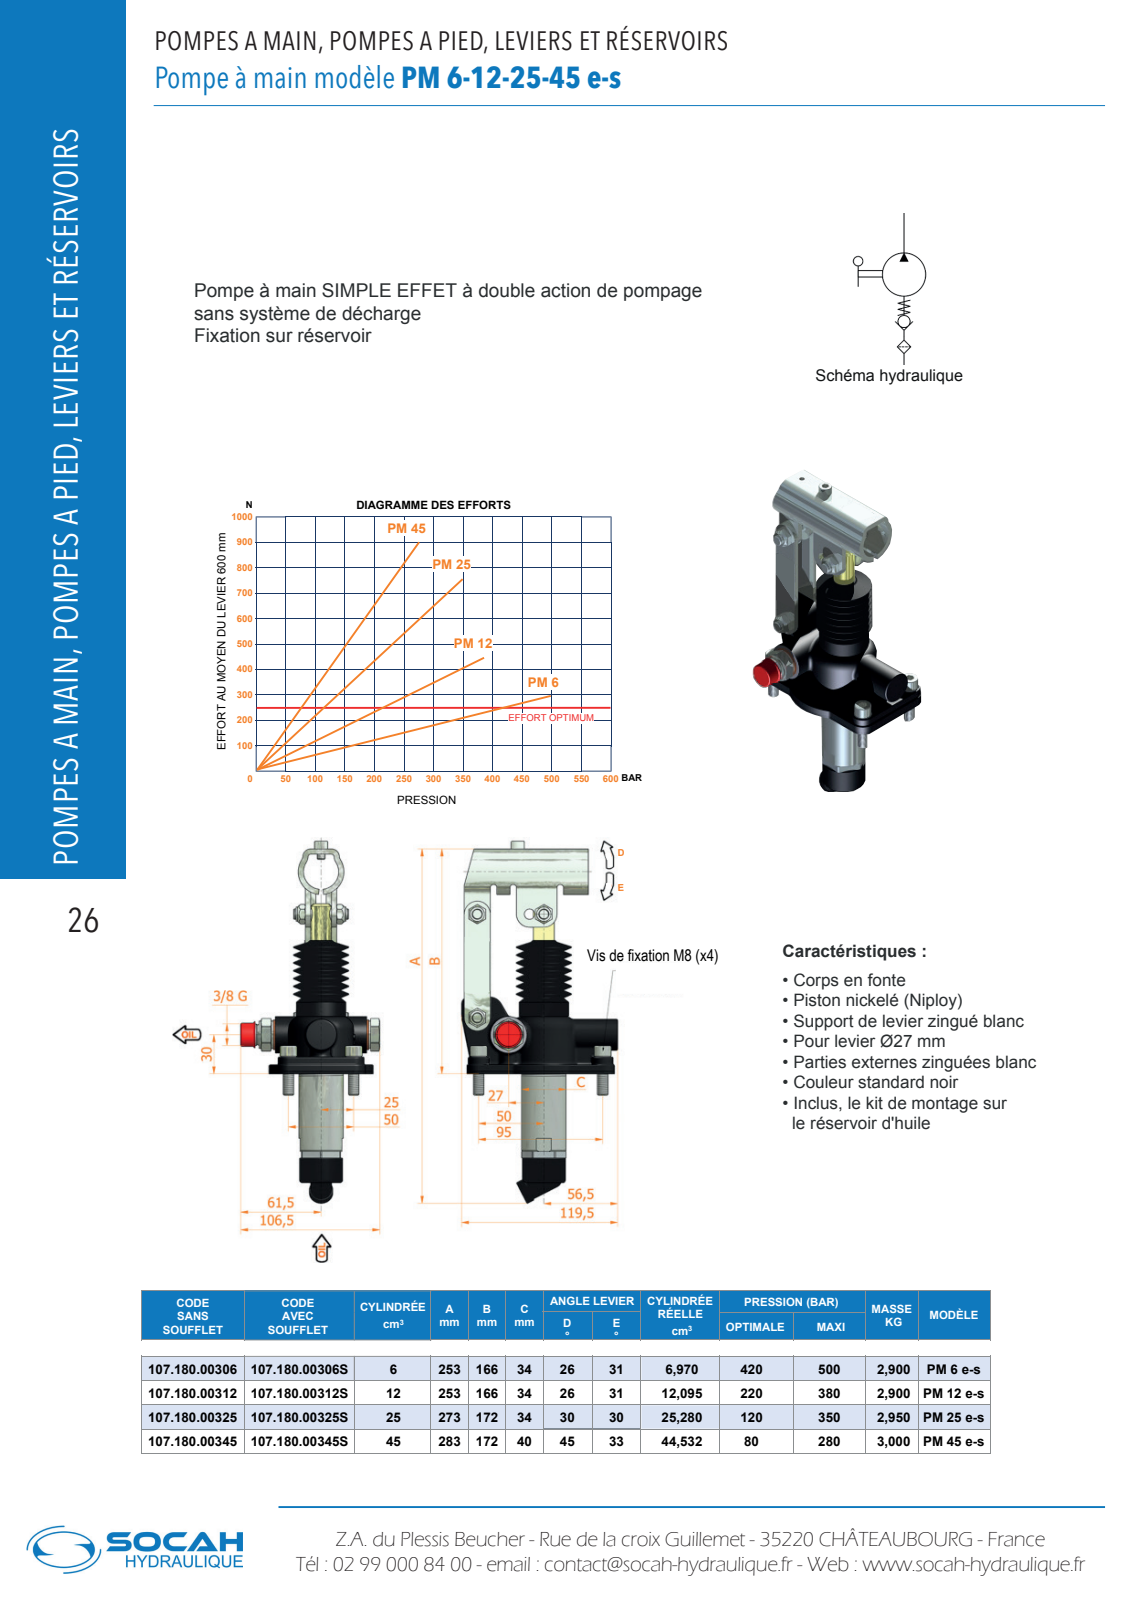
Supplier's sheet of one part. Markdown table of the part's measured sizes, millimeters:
| quantity | value |
| --- | --- |
| part name | Parte32 |
| STEP written by | Autodesk Inventor 2013 (AUTOMOTIVE_DESIGN) |
| units | millimeters |
| bodies | 12 solids, 1403 faces (652 planar, 307 cylindrical, 444 other) |
| overall size | 277.85 × 119.5 × 106.5 |
| volume | 270 859 mm³ |
| surface area | 132 806 mm² |
| round holes (diameter × count) | 8 × 6, 14 × 4, 4 × 1, 9 × 1, 10 × 1, 17 × 1, 22 × 1, 25 × 1, 29 × 1, 40 × 1 |
| round bosses / shafts (diameter × count) | 13 × 4, 12 × 4, 8.5 × 4, 18 × 3, 11.05 × 3, 8 × 3, 20 × 2, 16 × 2 |
| partial cylindrical surfaces (radius × count) | 1 × 25, 0.2 × 24, 3 × 17, 0.1 × 16, 2 × 16, 8 × 9, 0.36 × 6, 0.53 × 6 |
| main face-to-face distances | 4, 20, 16, 2, 5, 7, 24, 1, 26, 31 |
| hole center spacings | 25.5, 50, 51.48, 55.9, 93.41, 95, 107.35, 45 |
